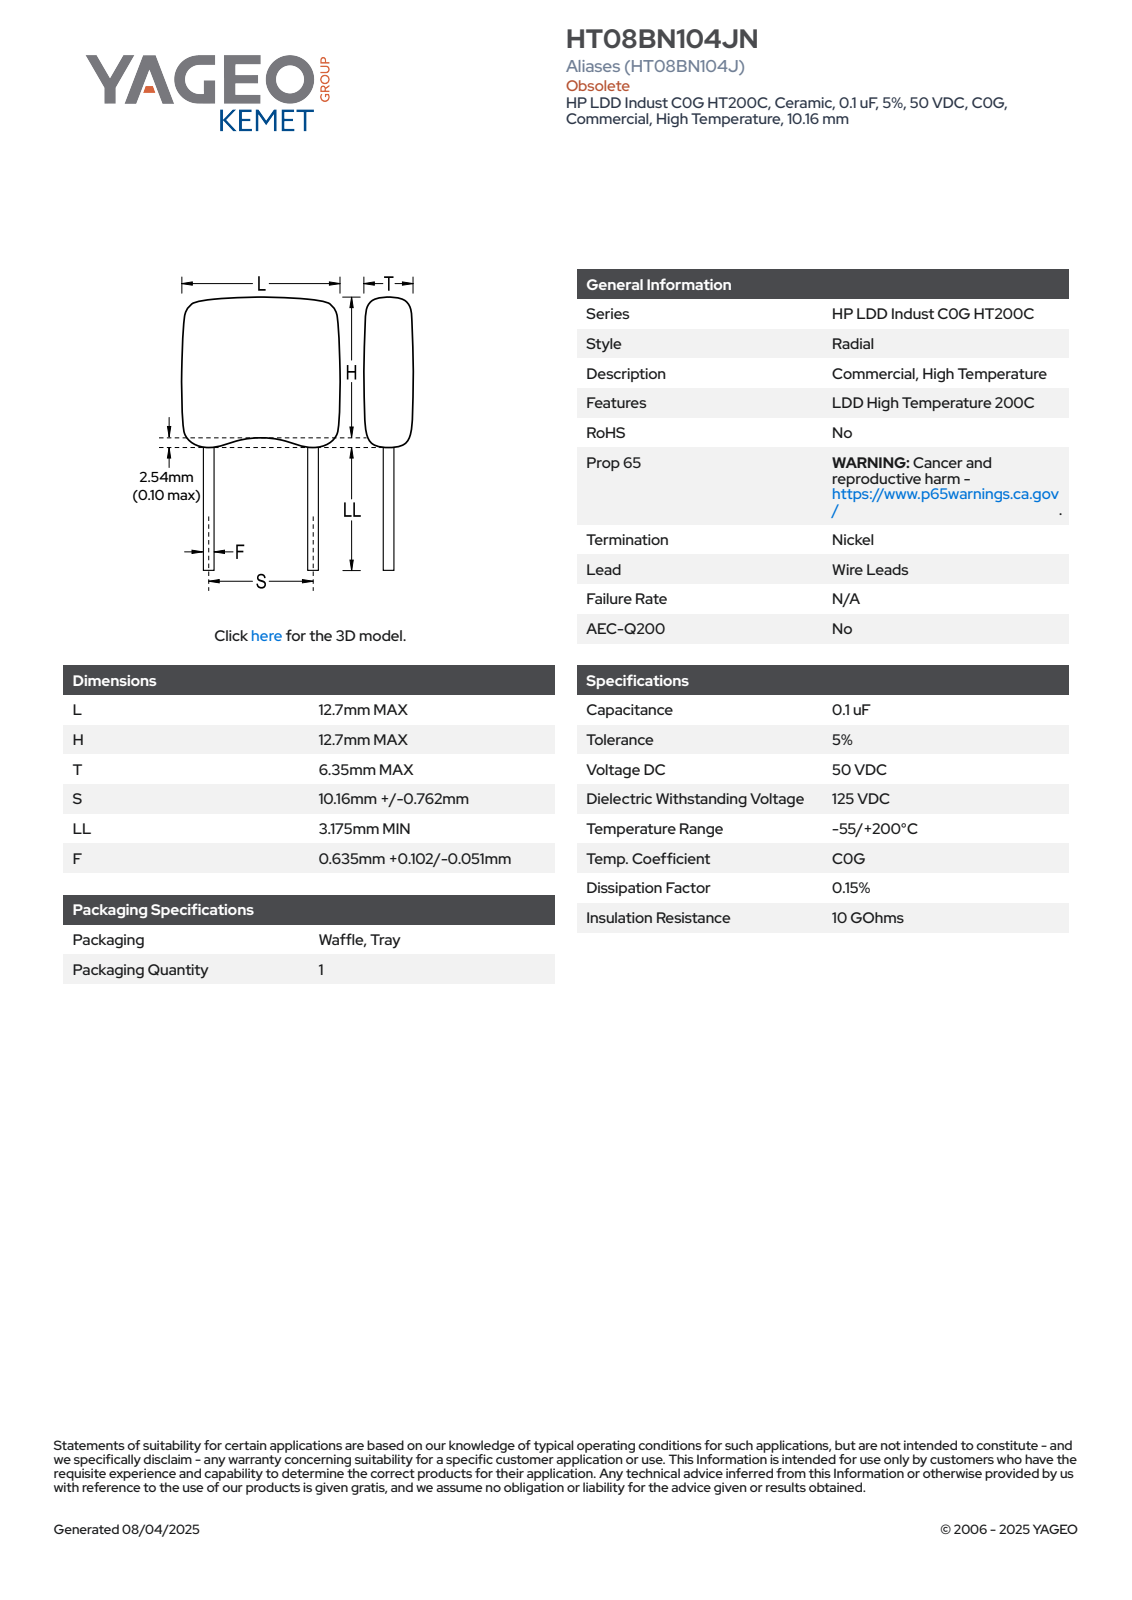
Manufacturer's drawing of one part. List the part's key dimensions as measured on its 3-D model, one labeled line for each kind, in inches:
Part name (STEP PRODUCT): CCR_RMST_HT08_L12.7H12.7T6.35S10.92LL31.75F0.635
STEP written by: SolidWorks 2014 (AUTOMOTIVE_DESIGN)
Units: inches
Bodies: 4 solids, 69 faces (65 planar, 4 cylindrical, 0 other)
Overall size (bounding box): 1.75 × 0.5 × 0.25
Volume: 0.064 in³ · Surface area: 1.23 in²
Round bosses / shafts (diameter × count): ⌀0.025 ×2
Main face-to-face distances: 0.25, 0.5, 1.25, 1.75, 1.542, 0.292, 0.208, 1.463, 0.213, 0.079
